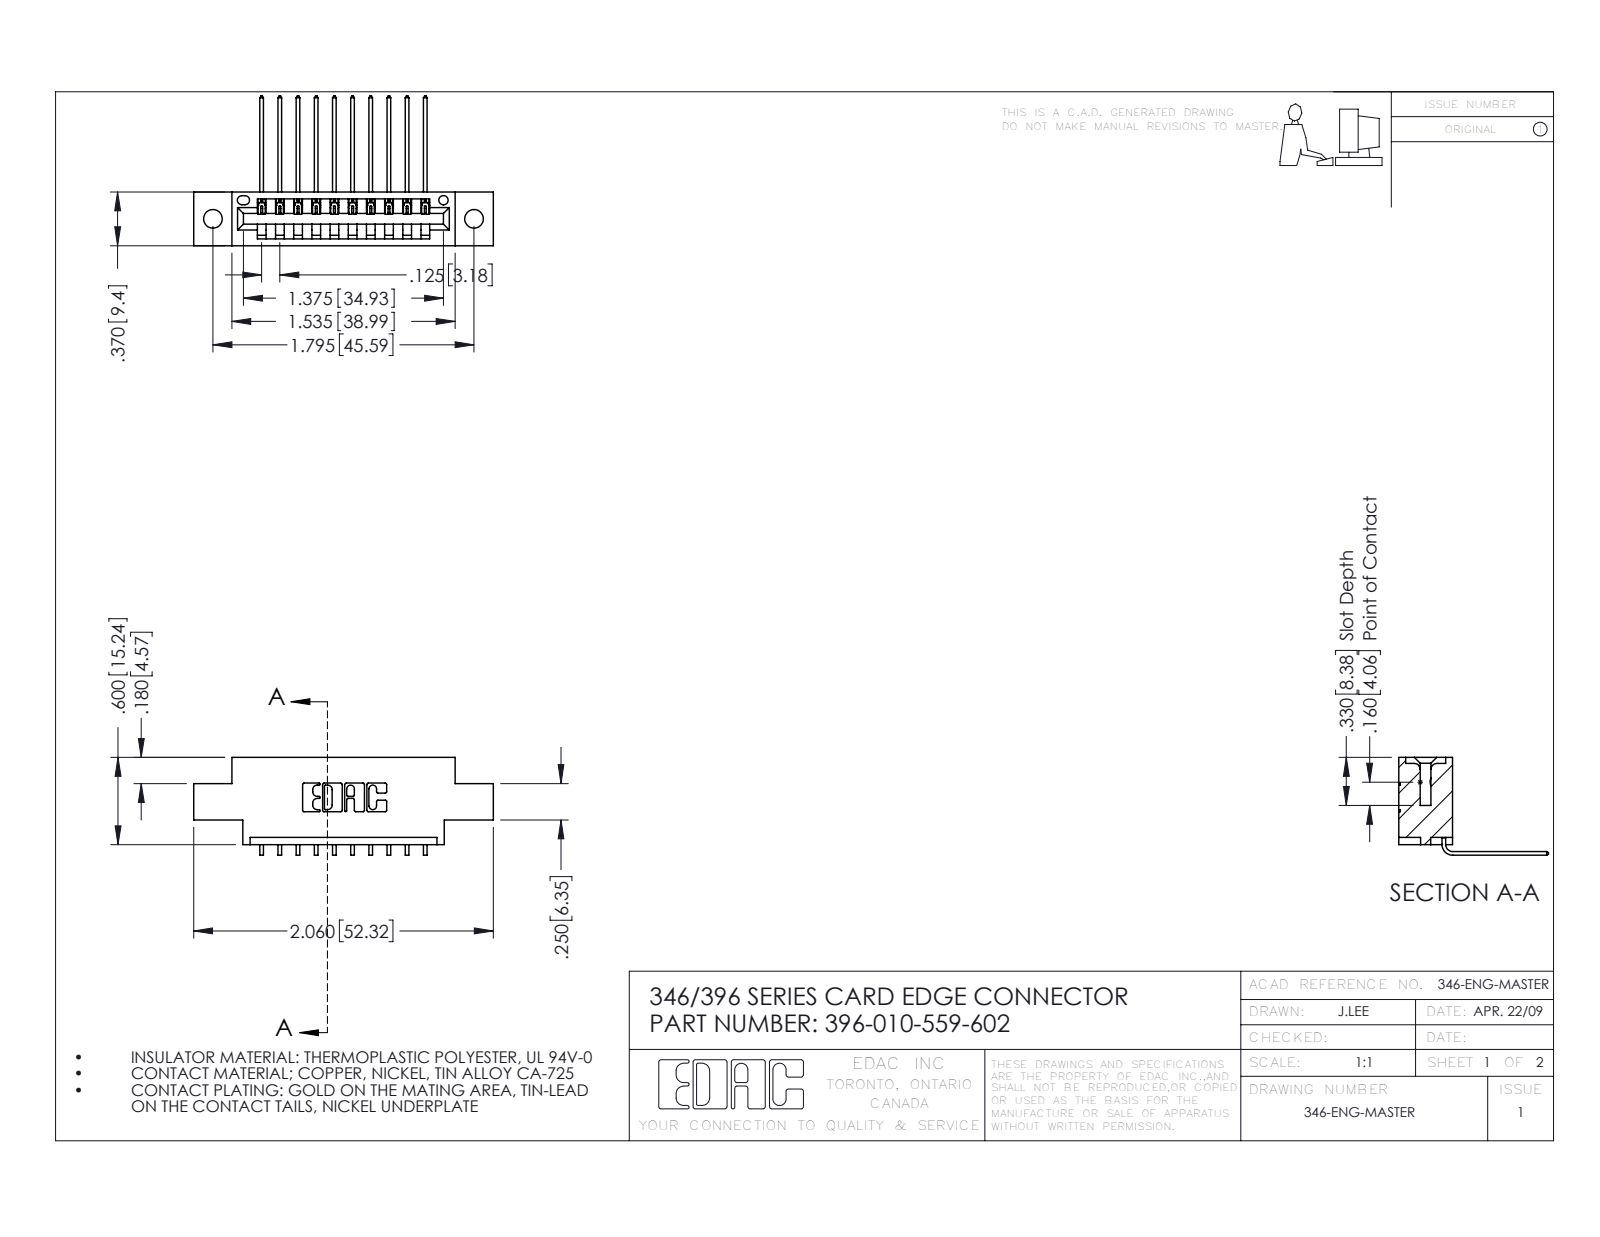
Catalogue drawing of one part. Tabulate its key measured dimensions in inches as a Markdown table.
| quantity | value |
| --- | --- |
| part name | 346 Part_0.170 Offset - 0.128 Dia; 345-292-001_558 559 Tail - 1; 396-010-559-602 |
| STEP written by | SolidWorks 2016 (CONFIG_CONTROL_DESIGN) |
| units | inches |
| bodies | 11 solids, 726 faces (500 planar, 226 cylindrical, 0 other) |
| overall size | 2.06 × 1.03 × 0.673 |
| volume | 0.283 in³ |
| surface area | 8.571 in² |
| round holes (diameter × count) | 0.128 × 2, 0.064 × 1 |
| partial cylindrical surfaces (radius × count) | 0.01 × 22, 0.006 × 20, 0.007 × 6, 0.031 × 6, 0.026 × 3, 0.031 × 2, 0.04 × 2, 0.014 × 1 |
| main face-to-face distances | 0.25, 0.37, 0.048, 0.322, 0.025, 0.072, 0.148, 0.222, 0.1, 0.174 |
| hole center spacings | 0.246, 1.59, 1.795 |
